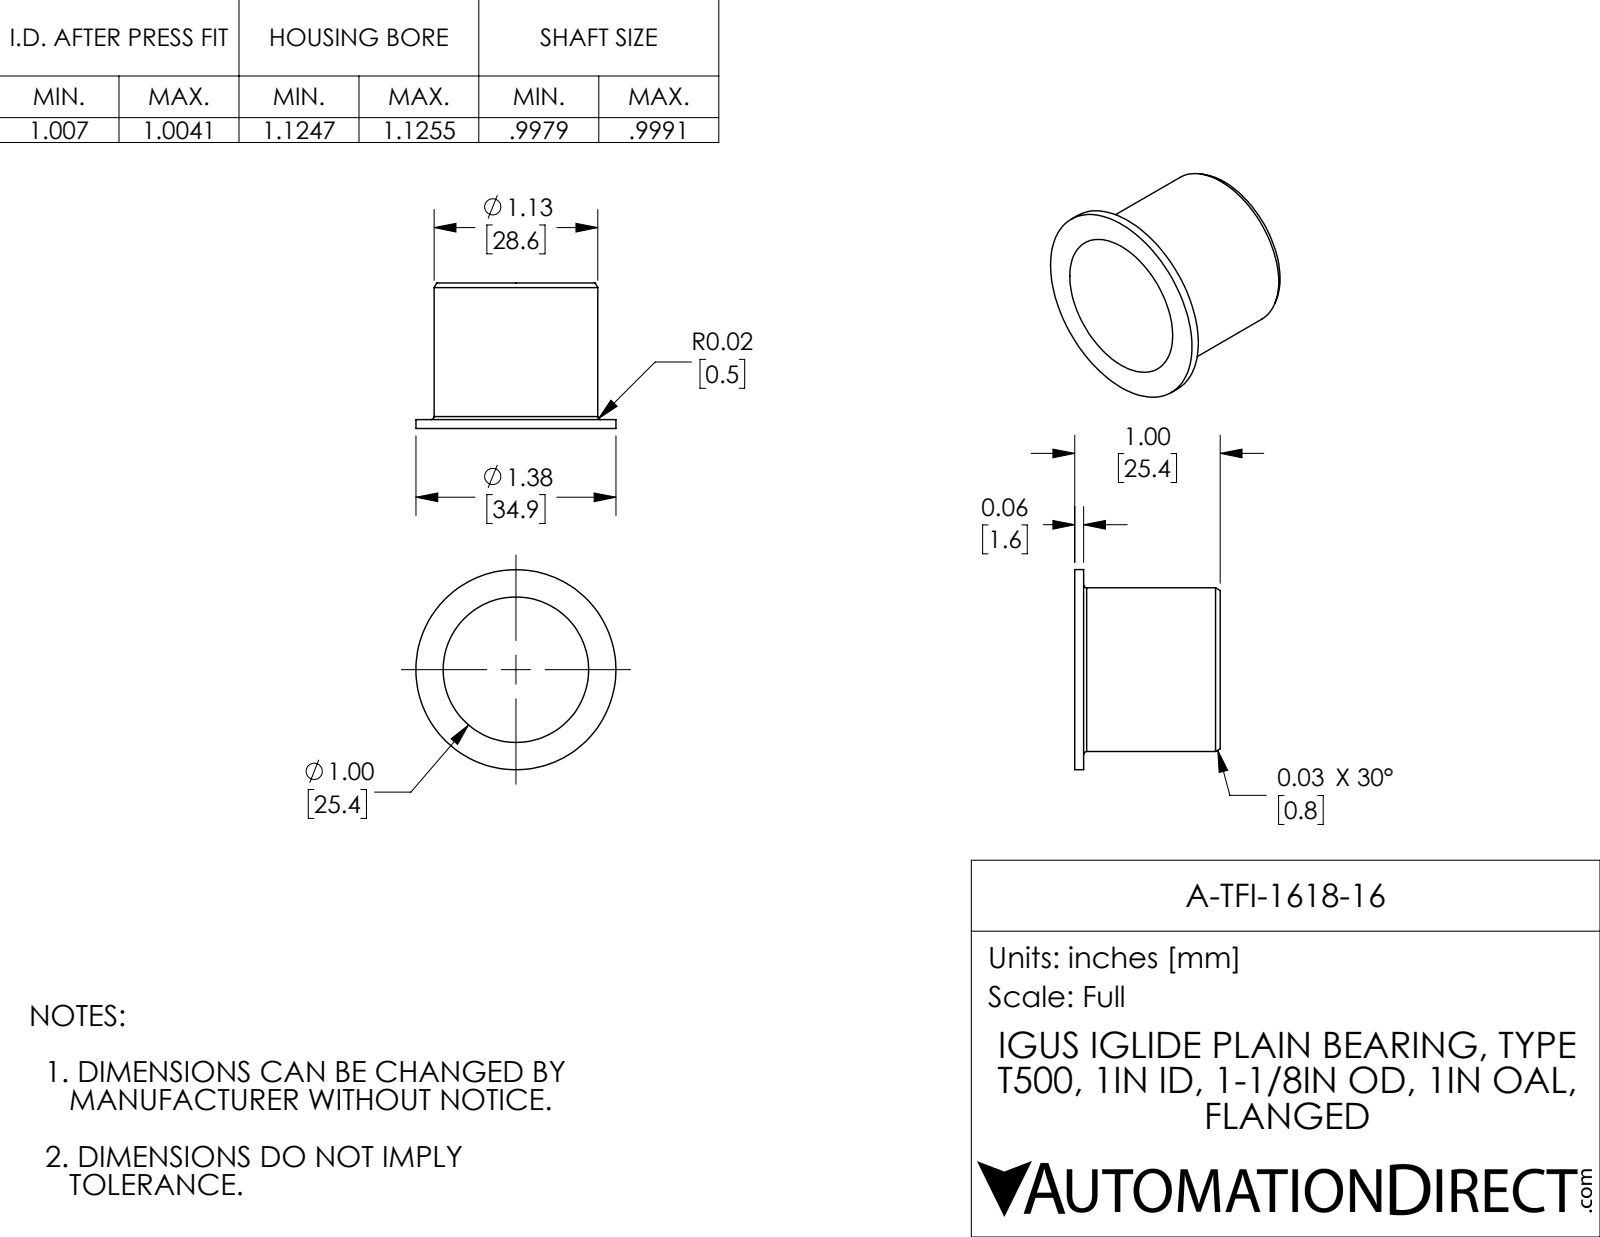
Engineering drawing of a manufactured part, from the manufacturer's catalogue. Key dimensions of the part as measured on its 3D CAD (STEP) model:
Part name (STEP PRODUCT): A-TFI-1618-16
STEP written by: SolidWorks 2017 (AUTOMOTIVE_DESIGN)
Units: inches
Bodies: 1 solid, 13 faces (3 planar, 6 cylindrical, 4 other)
Overall size (bounding box): 1.375 × 1.375 × 1
Volume: 0.238 in³ · Surface area: 8.047 in²
Round holes (diameter × count): ⌀1 ×1
Round bosses / shafts (diameter × count): ⌀1.375 ×1, ⌀1.125 ×1
Main face-to-face distances: 0.062, 1, 0.938
